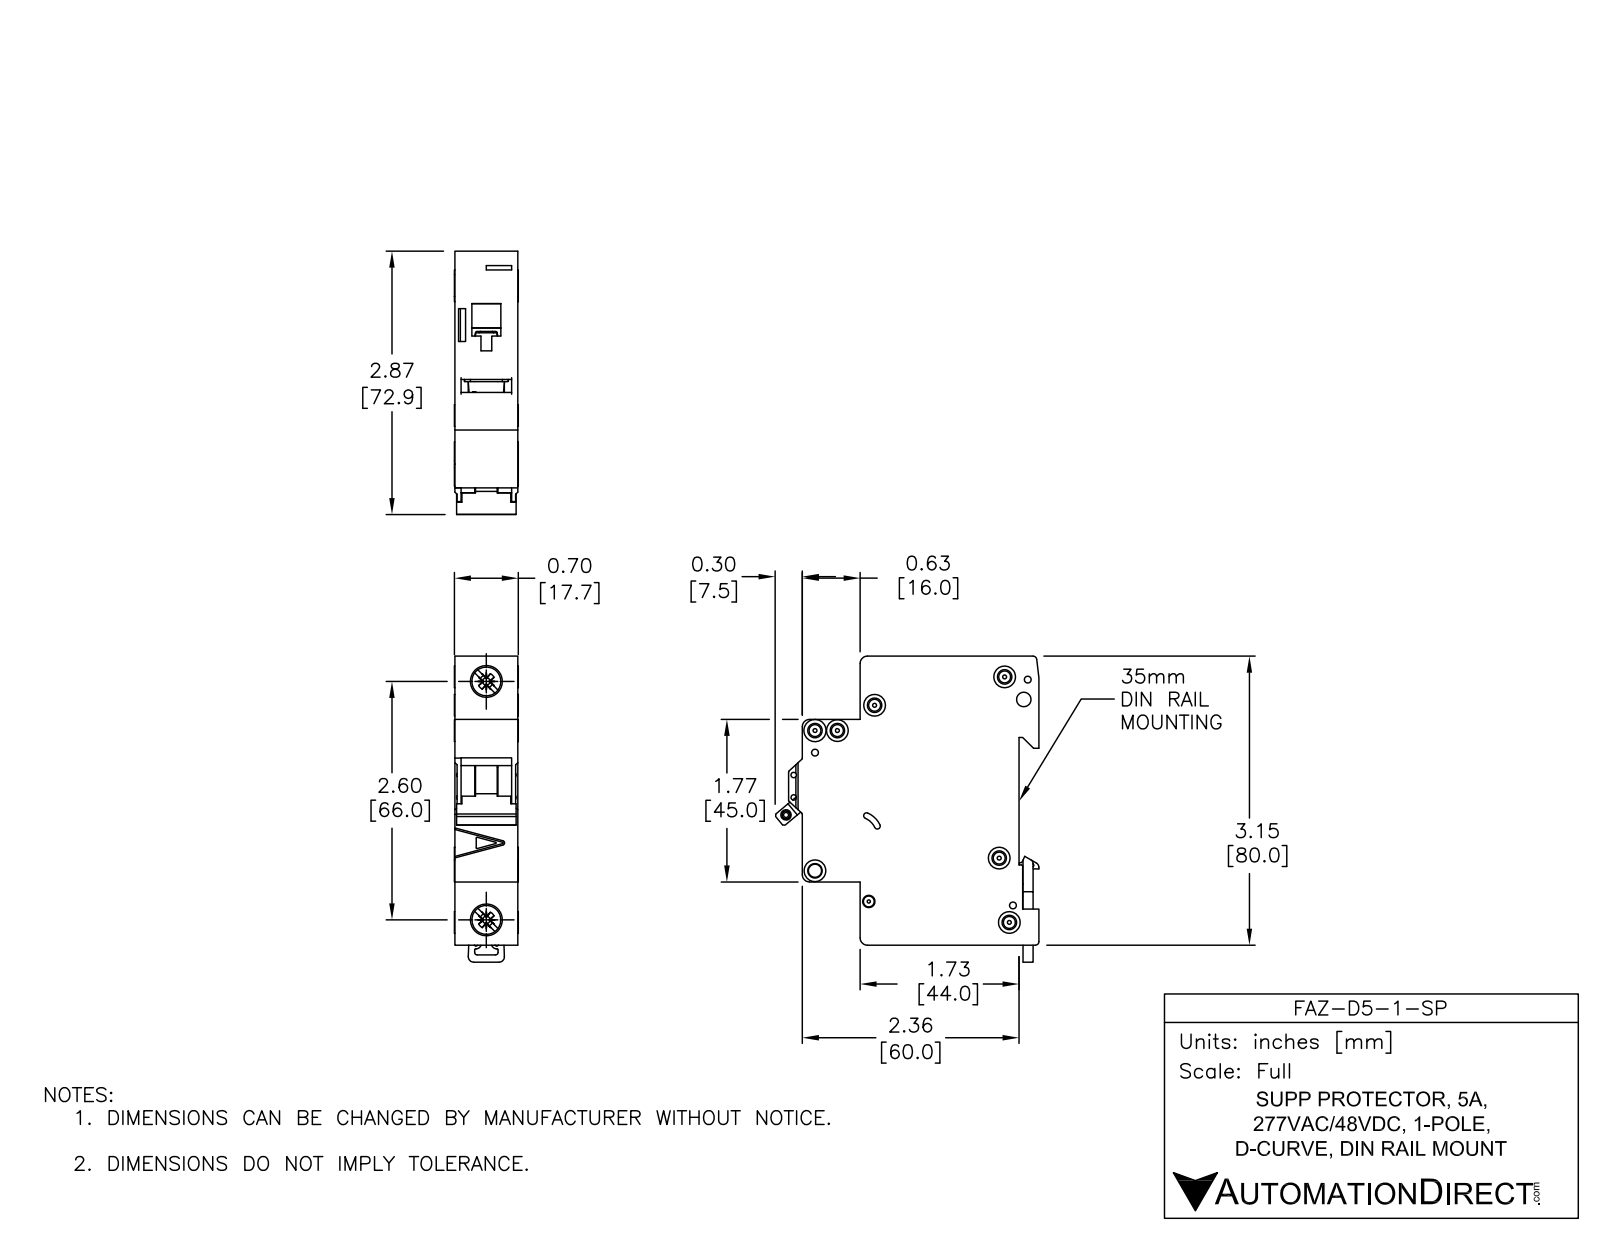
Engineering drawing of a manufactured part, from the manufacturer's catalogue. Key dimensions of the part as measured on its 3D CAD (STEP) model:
Part name (STEP PRODUCT): FAZ-D5-1-SP
STEP written by: SolidWorks 2014 (AUTOMOTIVE_DESIGN)
Units: millimetres
Bodies: 5 solids, 558 faces (235 planar, 202 cylindrical, 121 other)
Overall size (bounding box): 84.78 × 73.04 × 17.7
Volume: 74 935 mm³ · Surface area: 19 545 mm²
Round holes (diameter × count): ⌀3.6 ×6, ⌀1.9 ×3, ⌀1.09 ×2, ⌀1.5 ×2, ⌀4 ×2, ⌀7.15 ×2, ⌀2.15 ×1, ⌀2.2 ×1, ⌀2.55 ×1, ⌀3.3 ×1, ⌀3.4 ×1
Round bosses / shafts (diameter × count): ⌀6 ×4, ⌀8.2 ×2, ⌀2.5 ×1
Partial cylindrical surfaces — rounded edges, fillets, slot ends (radius × count): R0.25 ×30, R0.5 ×13, R2 ×8, R0.2 ×5, R1 ×4, R0.8 ×2, R3 ×2, R1.5 ×1
Main face-to-face distances: 17.5, 79.48, 5.5, 49.5, 44, 65.5, 60, 16, 1.75, 15.75
Hole centre spacings: 6.2, 13.64, 4.81, 5.19, 5.61, 6.1, 6.44, 8.19
